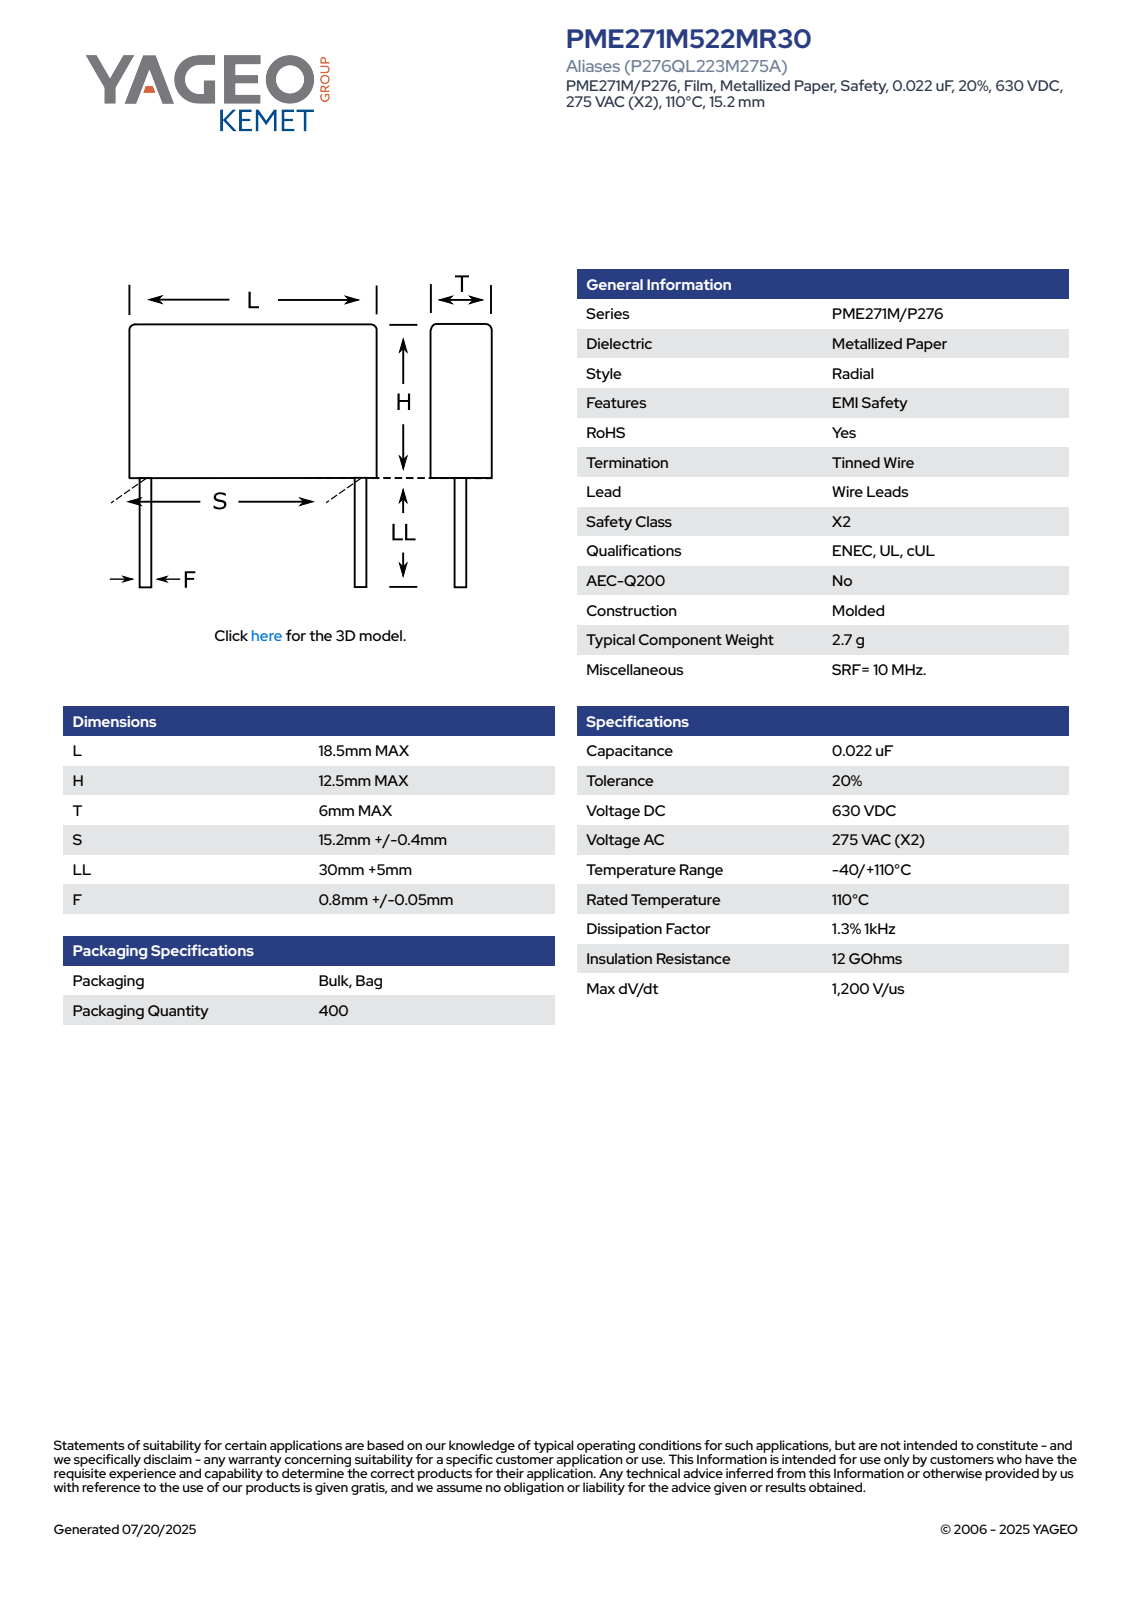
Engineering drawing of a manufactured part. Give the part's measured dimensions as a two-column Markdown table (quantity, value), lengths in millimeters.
| quantity | value |
| --- | --- |
| part name | CFR_MOLDED_18.5X12.5X6_L18.5H12.5T6S15.2LL35F0.85 |
| STEP written by | SolidWorks 2021 (AUTOMOTIVE_DESIGN) |
| units | millimeters |
| bodies | 4 solids, 73 faces (65 planar, 8 cylindrical, 0 other) |
| overall size | 47.5 × 18.5 × 6 |
| volume | 1 425 mm³ |
| surface area | 1 027 mm² |
| round bosses / shafts (diameter × count) | 0.85 × 2 |
| partial cylindrical surfaces (radius × count) | 0.5 × 4 |
| main face-to-face distances | 6, 12.5, 18.5, 35, 47.5, 41.9, 6.9, 5.6, 40.24, 5.24 |
